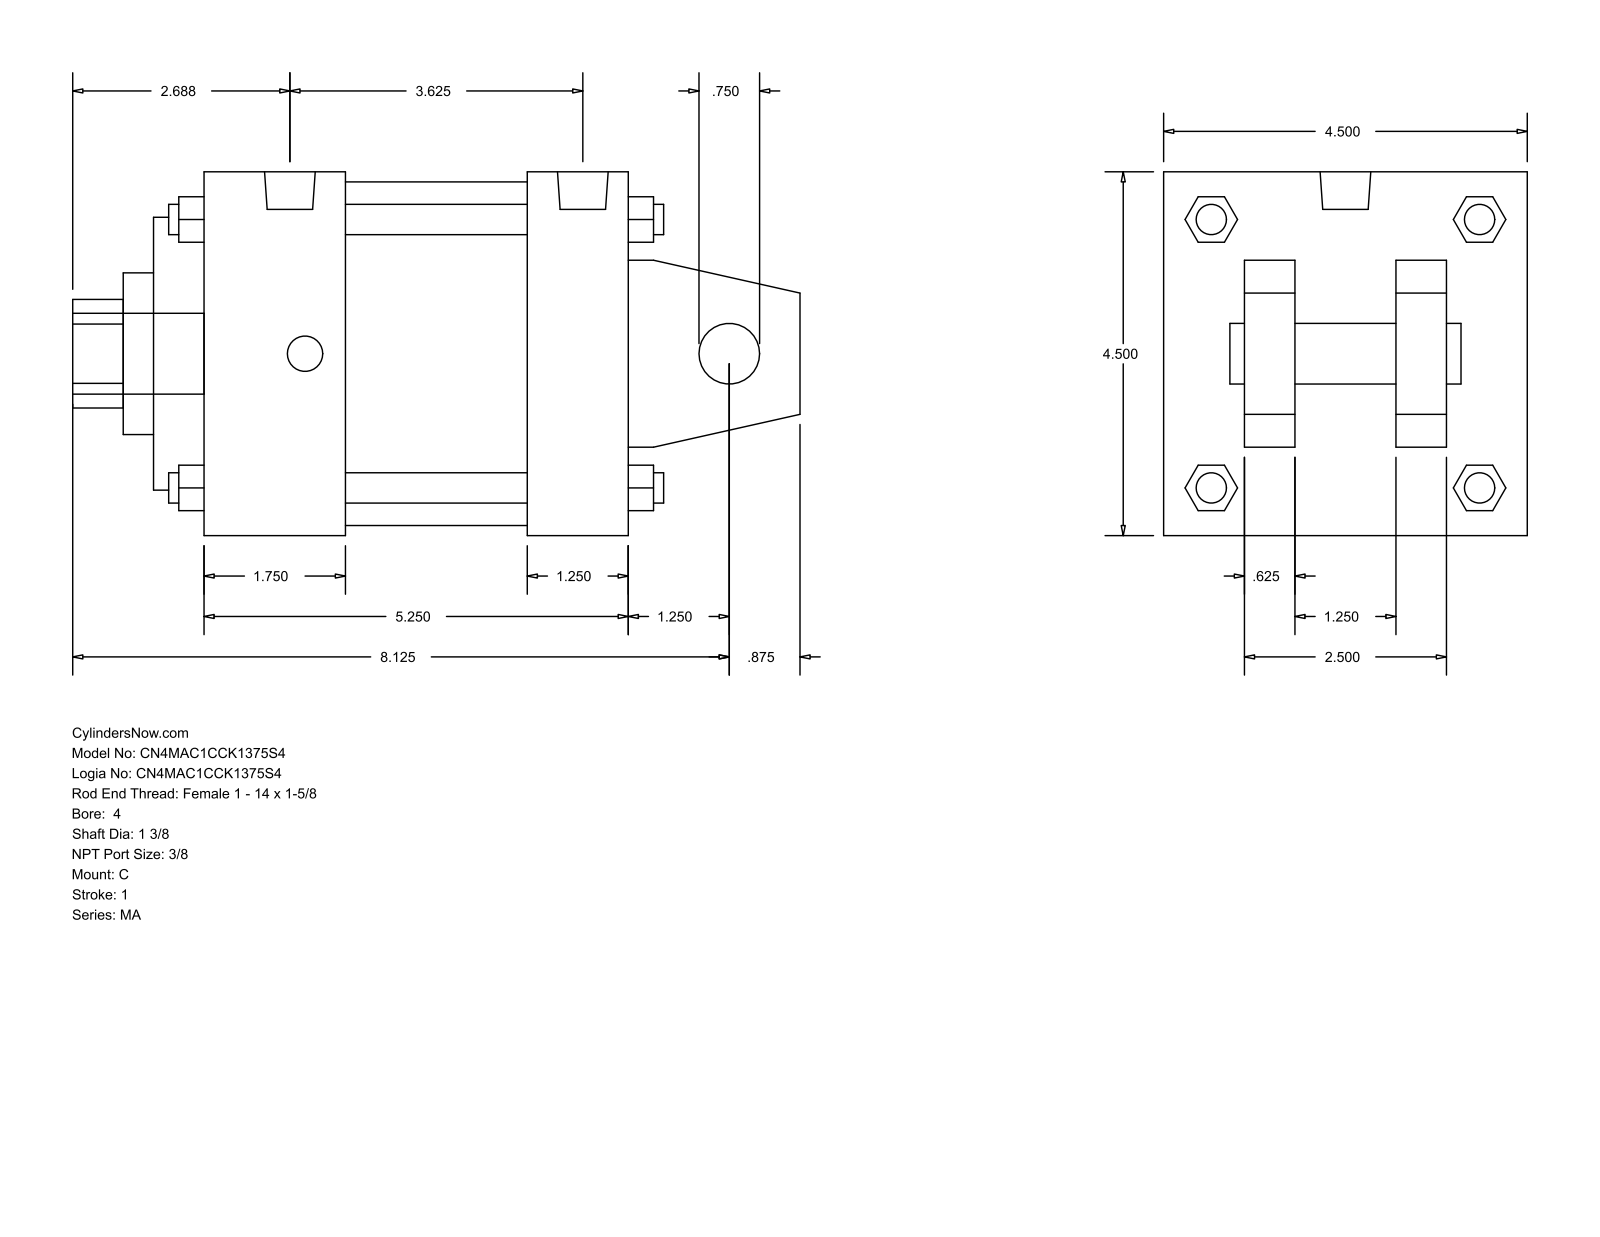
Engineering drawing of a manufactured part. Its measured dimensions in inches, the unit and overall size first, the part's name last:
Units: inches
Overall size (bounding box): 9 × 4.5 × 4.5
Round holes (diameter × count): ⌀0.75 ×1, ⌀1.375 ×1, ⌀2 ×1, ⌀3.375 ×1, ⌀4.25 ×1
Round bosses / shafts (diameter × count): ⌀0.437 ×4, ⌀0.375 ×4, ⌀0.627 ×2, ⌀1 ×1
Partial cylindrical surfaces — rounded edges, fillets, slot ends (radius × count): R0.672 ×1
Main face-to-face distances: 4.5, 0.625, 3.5, 5.25, 2.875, 1.625, 1, 1.875, 5.875, 4.625
Bodies: 0 solids, 141 faces (109 planar, 32 cylindrical, 0 other)
Part name (STEP PRODUCT): MA_C__0400_1.375
STEP written by: GSSL Pune (CONFIG_CONTROL_DESIGN)
